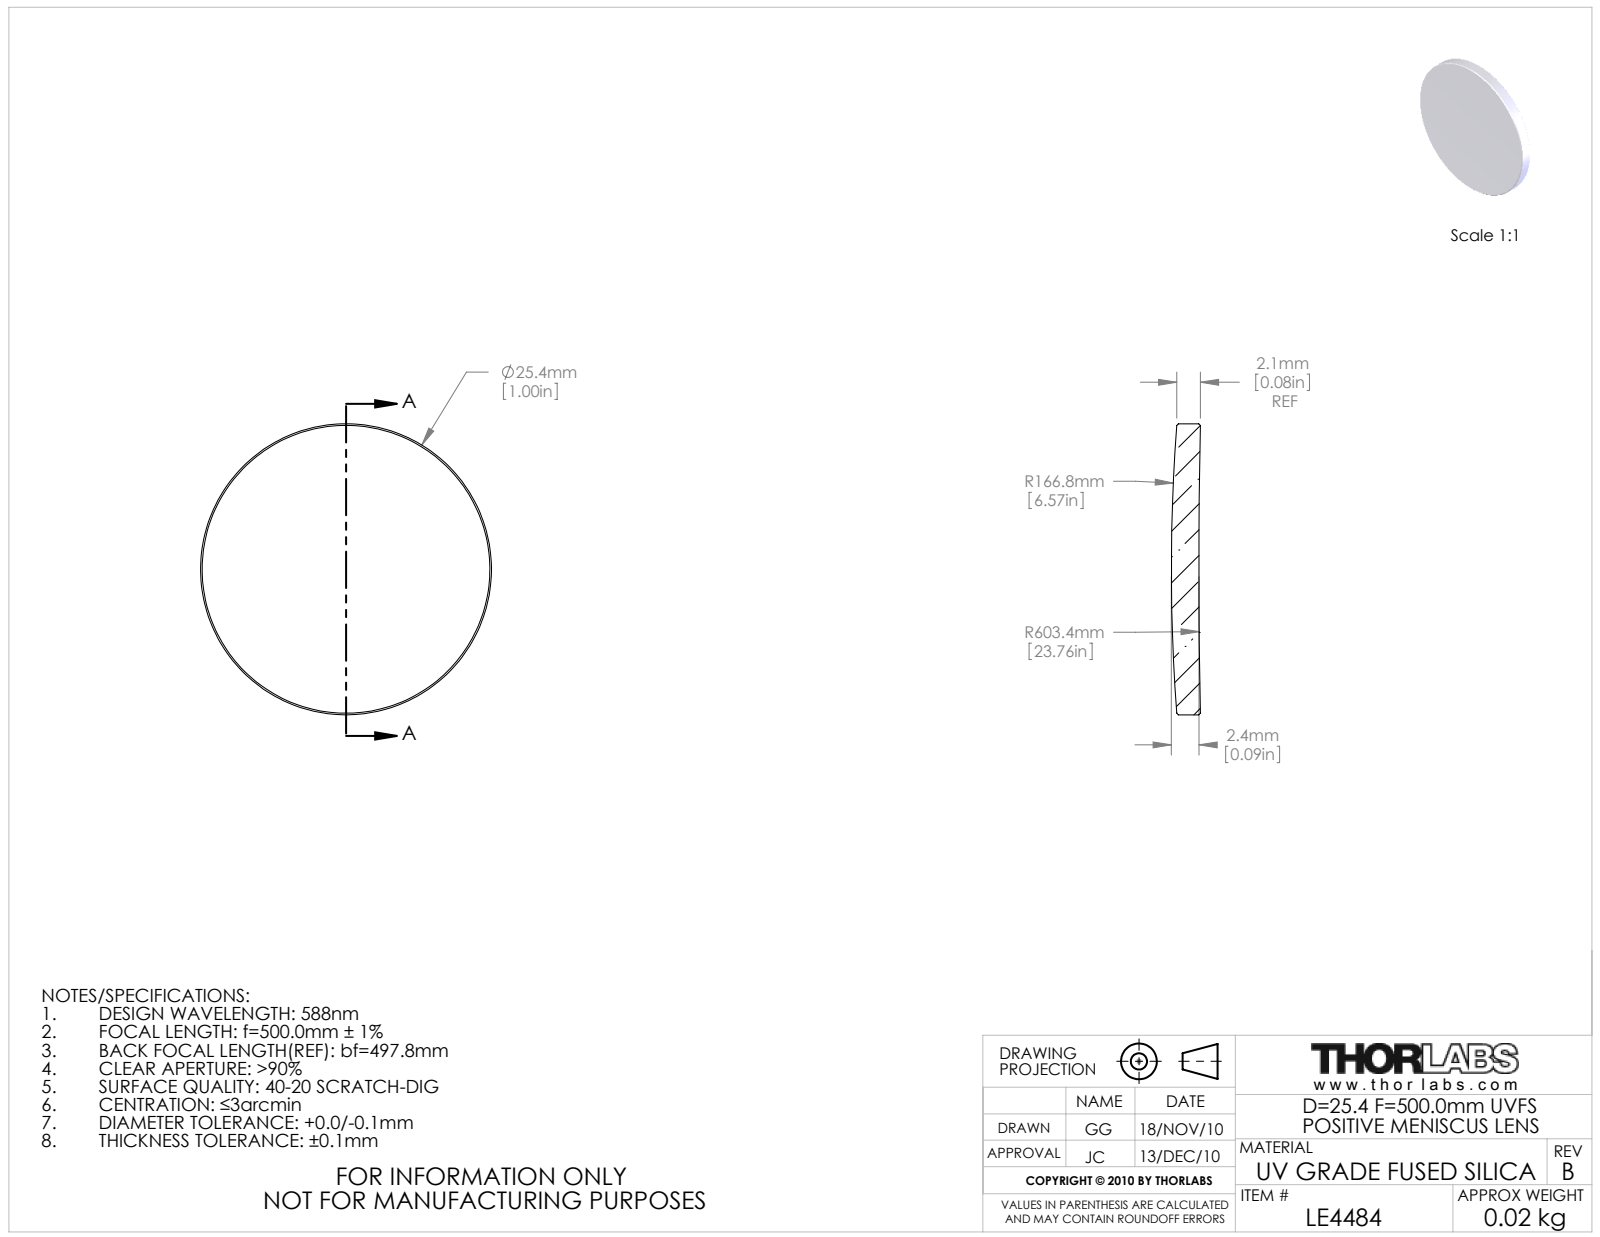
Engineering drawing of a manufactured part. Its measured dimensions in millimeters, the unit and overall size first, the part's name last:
Units: millimetres
Overall size (bounding box): 25.4 × 25.4 × 2.53
Round bosses / shafts (diameter × count): ⌀25.4 ×1
Volume: 1 126 mm³ · Surface area: 1 165 mm²
Bodies: 1 solid, 10 faces (0 planar, 2 cylindrical, 8 other)
Part name (STEP PRODUCT): 4209-E0W
STEP written by: SolidWorks 2009 (AUTOMOTIVE_DESIGN)
